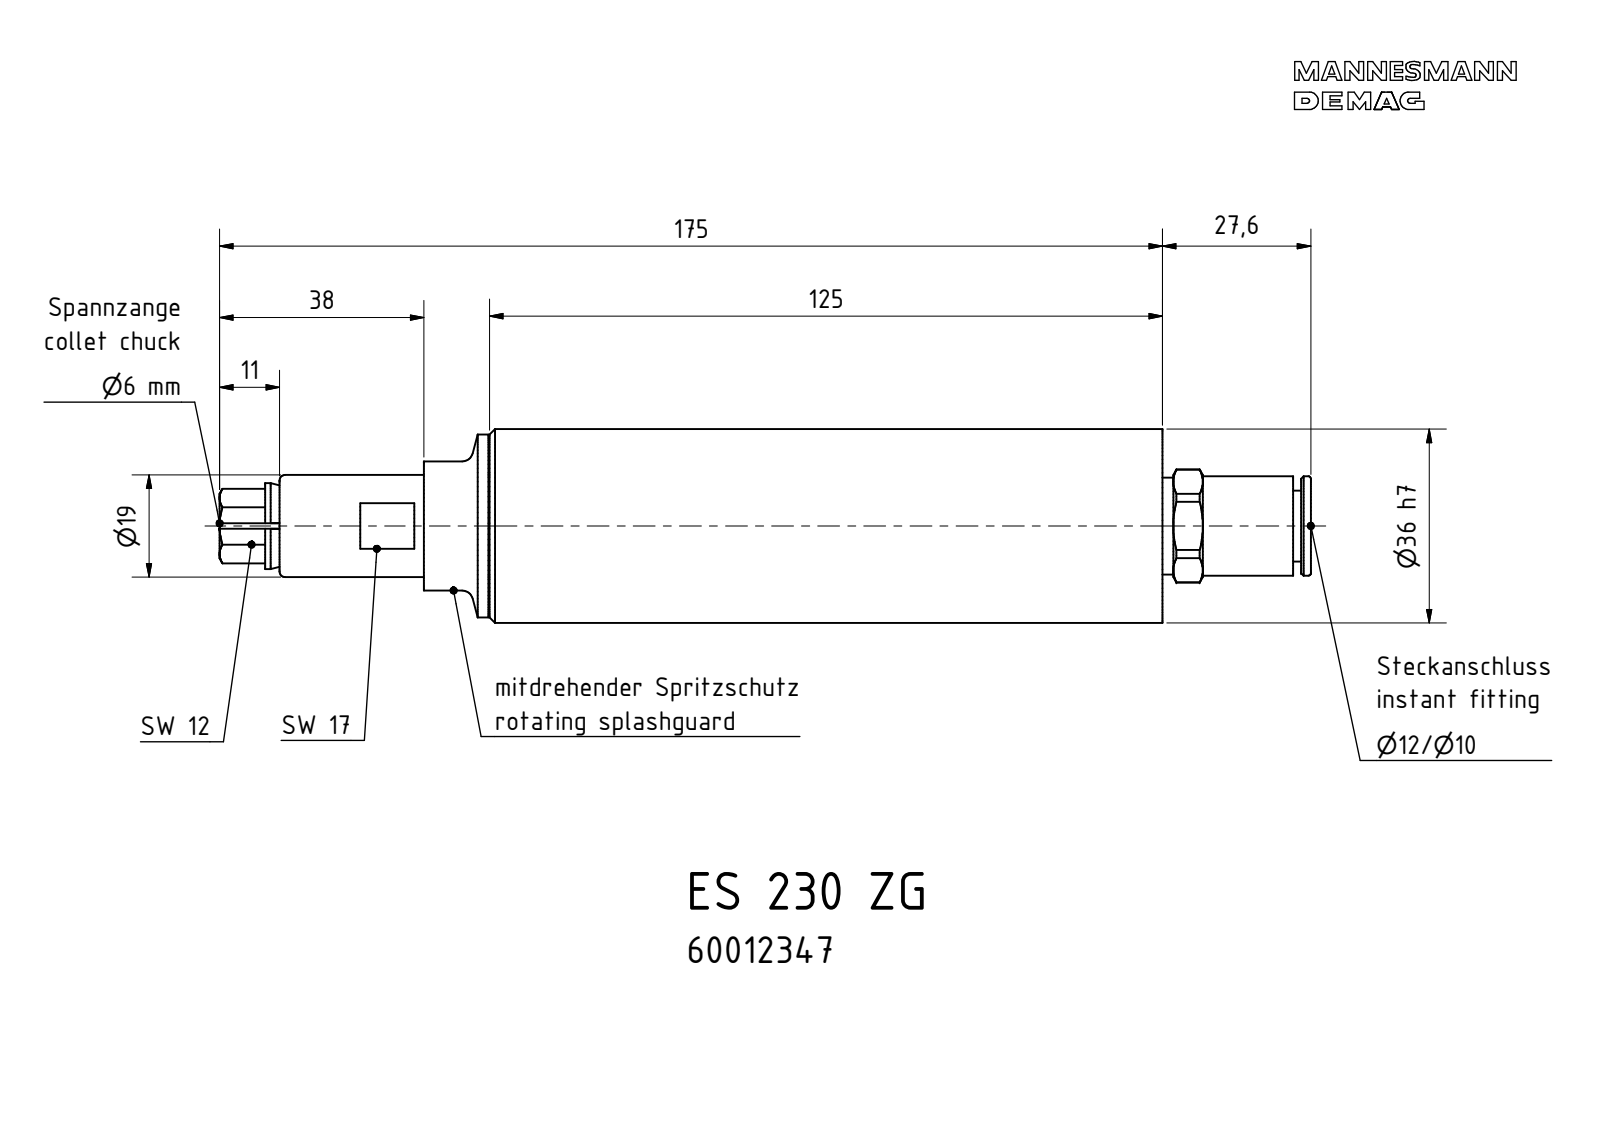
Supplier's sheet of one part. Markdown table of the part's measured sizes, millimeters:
| quantity | value |
| --- | --- |
| part name | ES 230 ZG_60012347 |
| STEP written by | Autodesk Inventor 2008 (CONFIG_CONTROL_DESIGN) |
| units | millimeters |
| bodies | 1 solid, 132 faces (65 planar, 30 cylindrical, 37 other) |
| overall size | 202.71 × 36 × 36 |
| volume | 144 811 mm³ |
| surface area | 25 153 mm² |
| round holes (diameter × count) | 6 × 1, 8.5 × 1, 12 × 1, 19.5 × 1 |
| round bosses / shafts (diameter × count) | 36 × 1, 34 × 1, 24 × 1, 19 × 1, 18.5 × 1, 18 × 1, 16 × 1, 13.2 × 1 |
| partial cylindrical surfaces (radius × count) | 15 × 3, 4.54 × 1, 10.5 × 1 |
| main face-to-face distances | 125, 0.5, 125.5, 3.5, 12, 1, 15.5, 2.5, 11.7, 12.2 |
